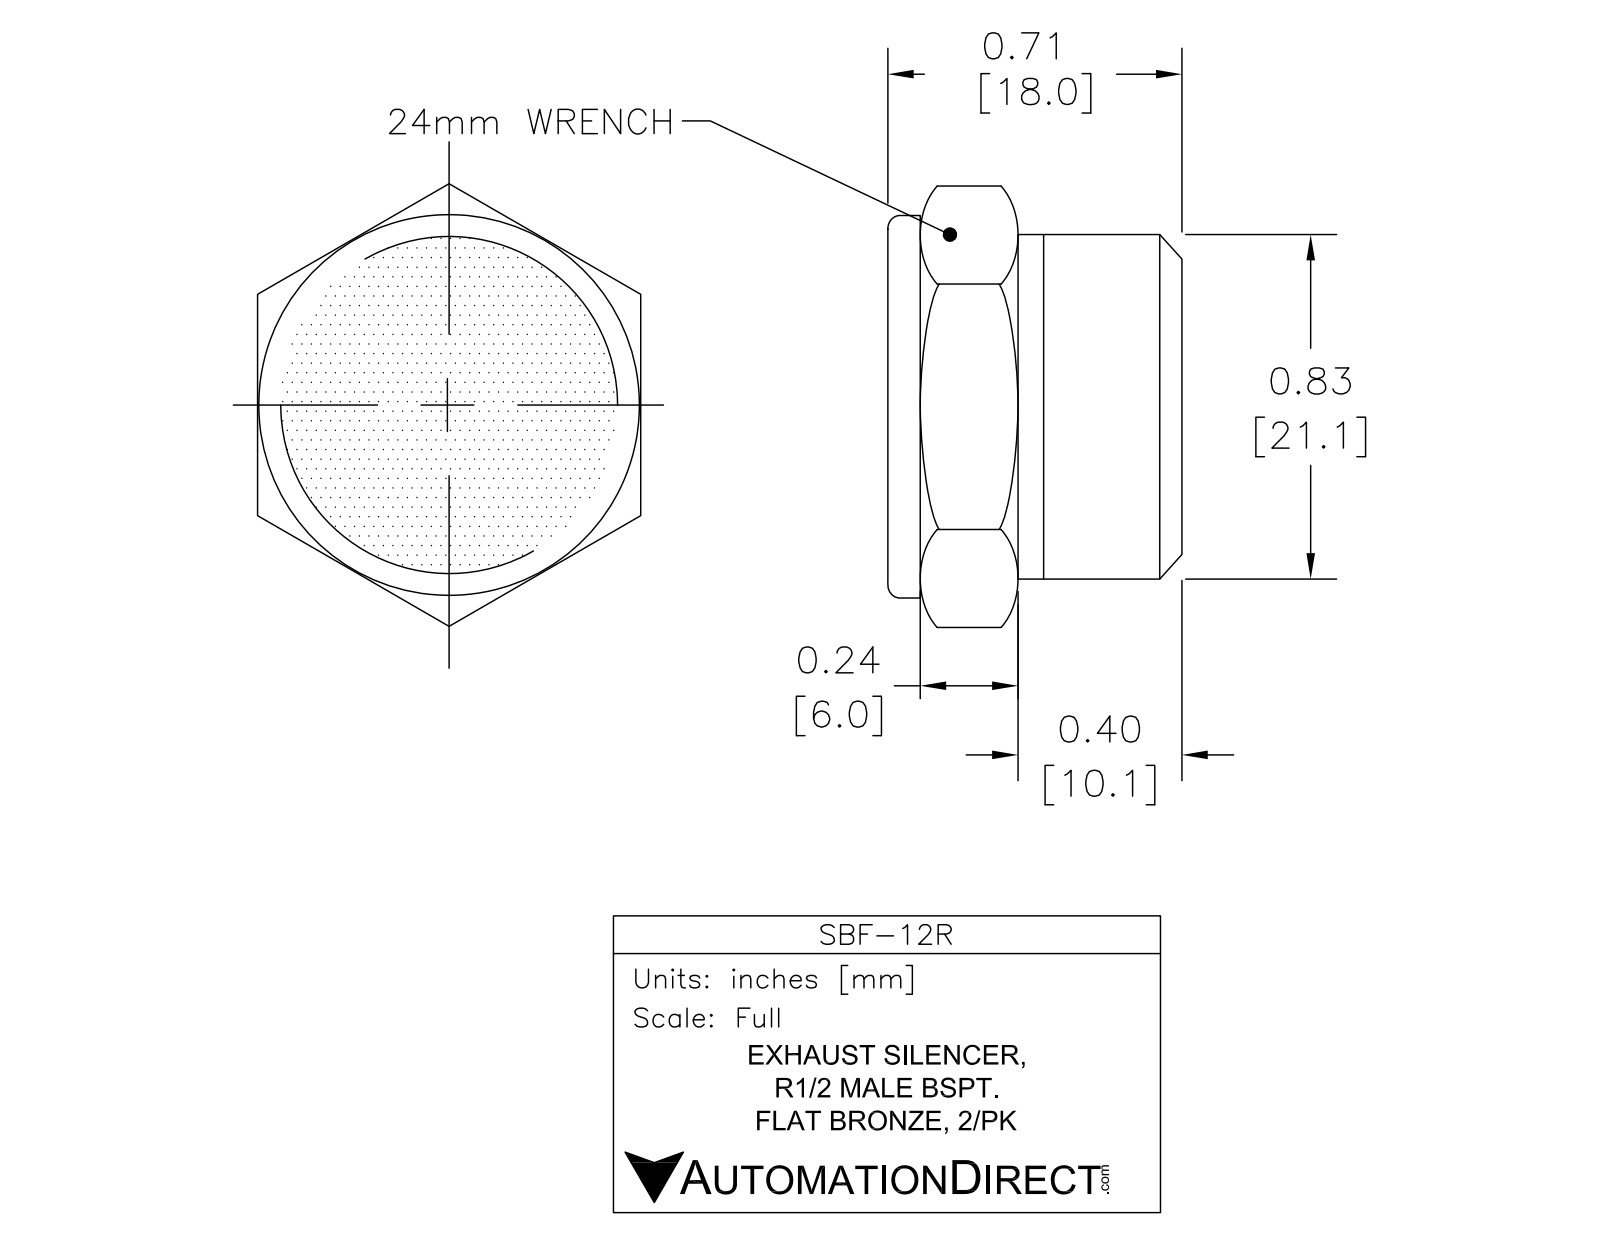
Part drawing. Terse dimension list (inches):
name: SBF-12R
written by: SolidWorks 2015 (CONFIG_CONTROL_DESIGN)
unit: in
bodies: 1 solid, 48 faces (13 planar, 15 cylindrical, 20 other)
size: 0.94 × 0.814 × 0.71
volume: 0.211 in³; area: 4.21 in²
holes: 1× ⌀0.44
bosses: 1× ⌀0.78, 1× ⌀0.703
face distances: 0.814, 0.71, 0.6, 0.11, 0.4, 0.2, 0.31, 0.37, 0.03, 0.23
